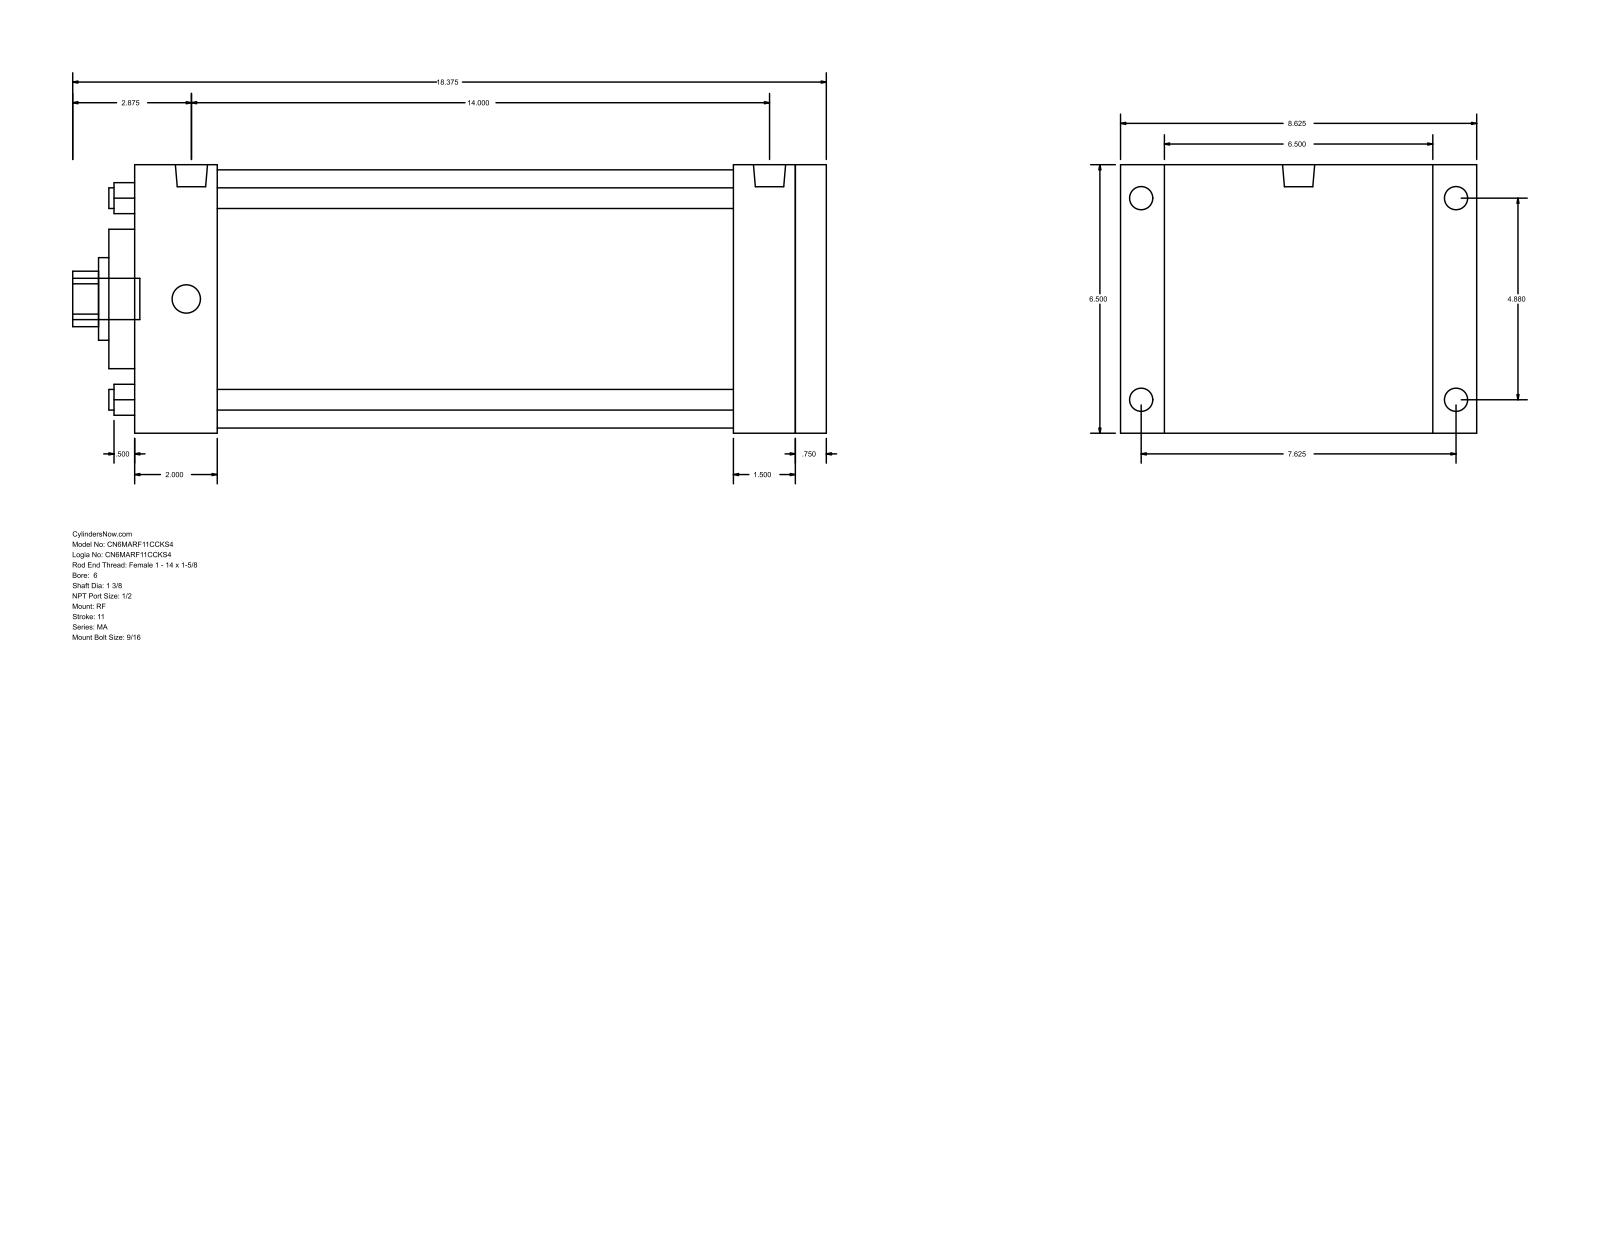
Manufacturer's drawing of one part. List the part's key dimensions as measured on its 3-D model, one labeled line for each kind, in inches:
Part name (STEP PRODUCT): MA_RF__0600_1.375
STEP written by: GSSL Pune (CONFIG_CONTROL_DESIGN)
Units: inches
Bodies: 0 solids, 94 faces (65 planar, 29 cylindrical, 0 other)
Overall size (bounding box): 18.375 × 8.625 × 6.5
Round holes (diameter × count): ⌀0.5 ×4, ⌀1.375 ×1, ⌀2 ×1, ⌀3.375 ×1, ⌀6.25 ×1
Round bosses / shafts (diameter × count): ⌀0.687 ×4, ⌀0.563 ×4, ⌀0.778 ×2, ⌀1 ×1
Partial cylindrical surfaces — rounded edges, fillets, slot ends (radius × count): R0.672 ×1
Main face-to-face distances: 6.5, 16.875, 0.75, 16.125, 2, 14.125, 14.875, 14.625, 12.625, 1.5
Hole centre spacings: 3.451, 4.88, 6.902
